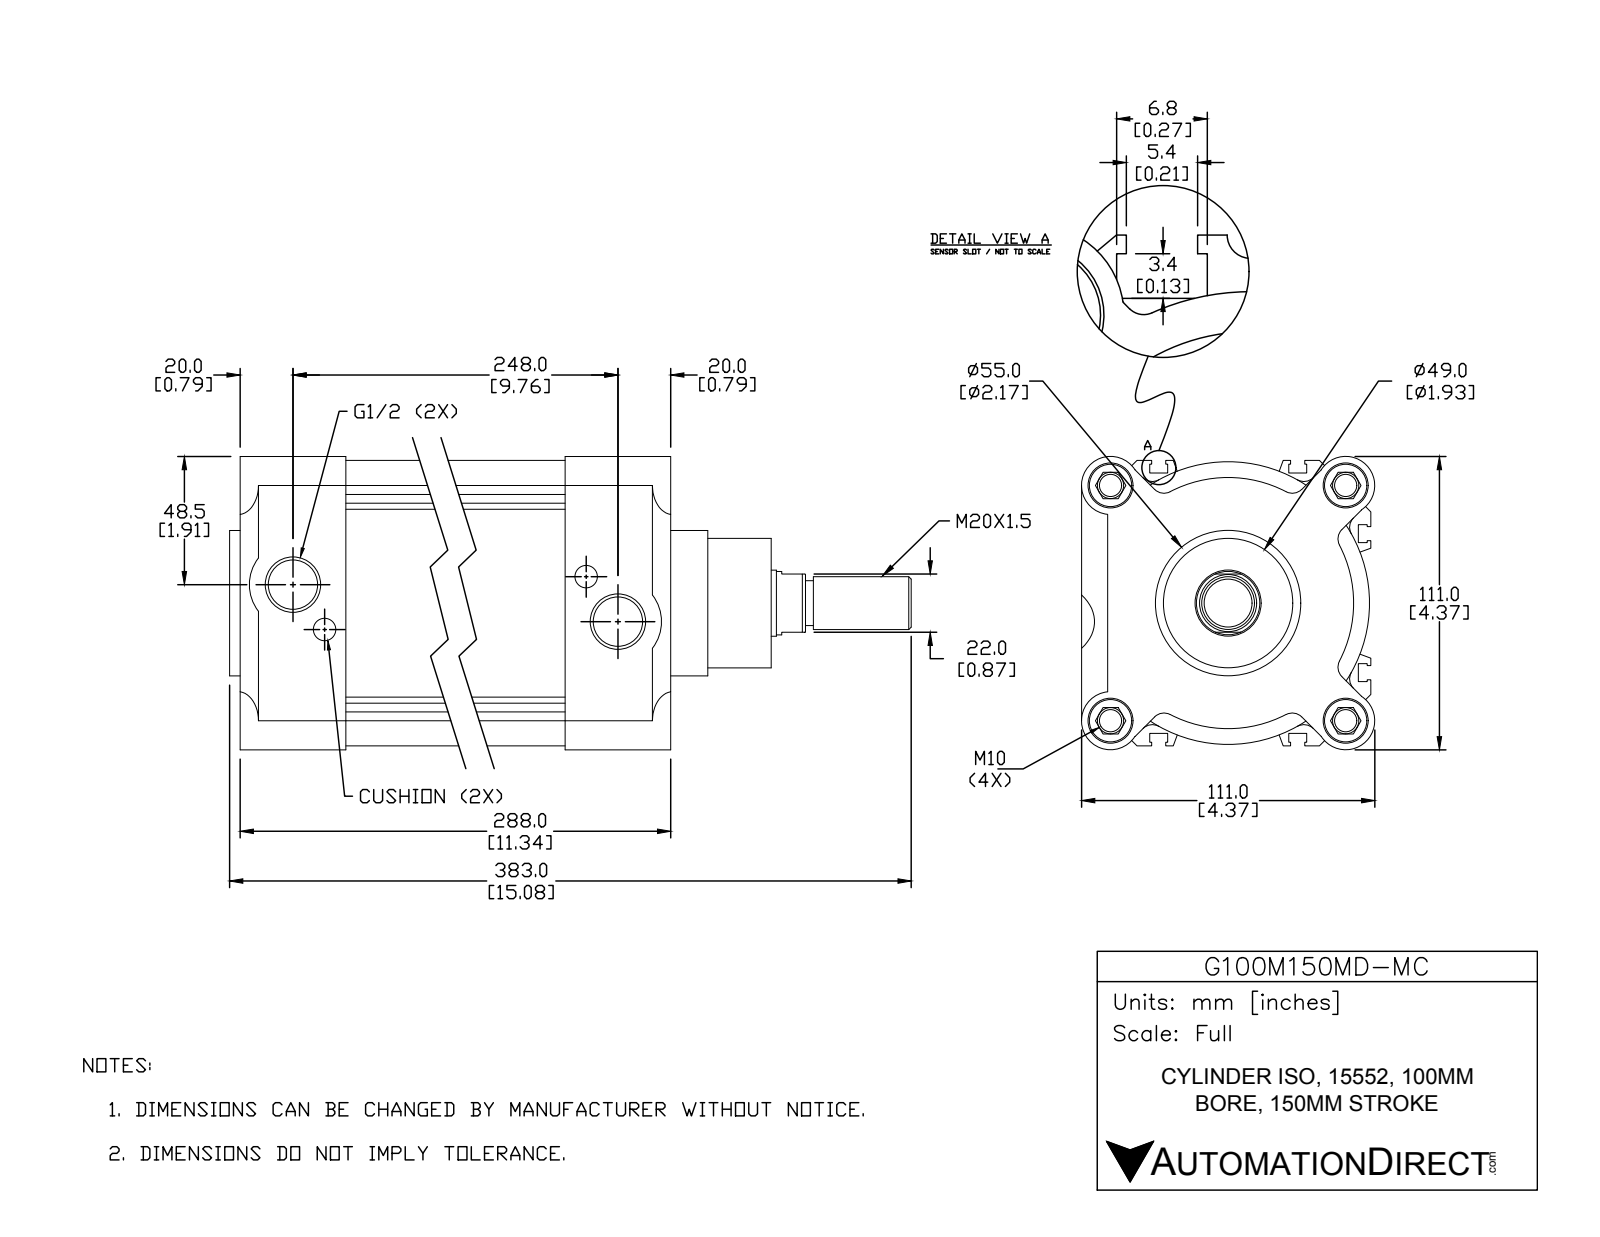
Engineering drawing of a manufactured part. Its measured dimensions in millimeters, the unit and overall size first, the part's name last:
Units: millimetres
Overall size (bounding box): 383 × 111 × 111
Round holes (diameter × count): ⌀8.4 ×4, ⌀17 ×4, ⌀8.5 ×2, ⌀18.6 ×2, ⌀25 ×1
Round bosses / shafts (diameter × count): ⌀16 ×4, ⌀100 ×1, ⌀55 ×1, ⌀49 ×1, ⌀24 ×1, ⌀20 ×1, ⌀17 ×1
Partial cylindrical surfaces — rounded edges, fillets, slot ends (radius × count): R5 ×12, R0.1 ×6, R9.5 ×4, R11 ×4, R16.5 ×2, R47.5 ×1, R53 ×1, R53.5 ×1
Main face-to-face distances: 238, 10, 198, 40, 50, 248, 38, 4.7, 88, 188
Hole centre spacings: 62.9, 89, 20.8, 125.9, 236, 224.9, 248.4
Volume: 2 096 000 mm³ · Surface area: 359 100 mm²
Bodies: 4 solids, 462 faces (248 planar, 162 cylindrical, 52 other)
Part name (STEP PRODUCT): 100-150-120.5-B; 100121-HR; 100-HL; G100M150MD-MC (+1 more)
STEP written by: SolidWorks 2015 (CONFIG_CONTROL_DESIGN)
